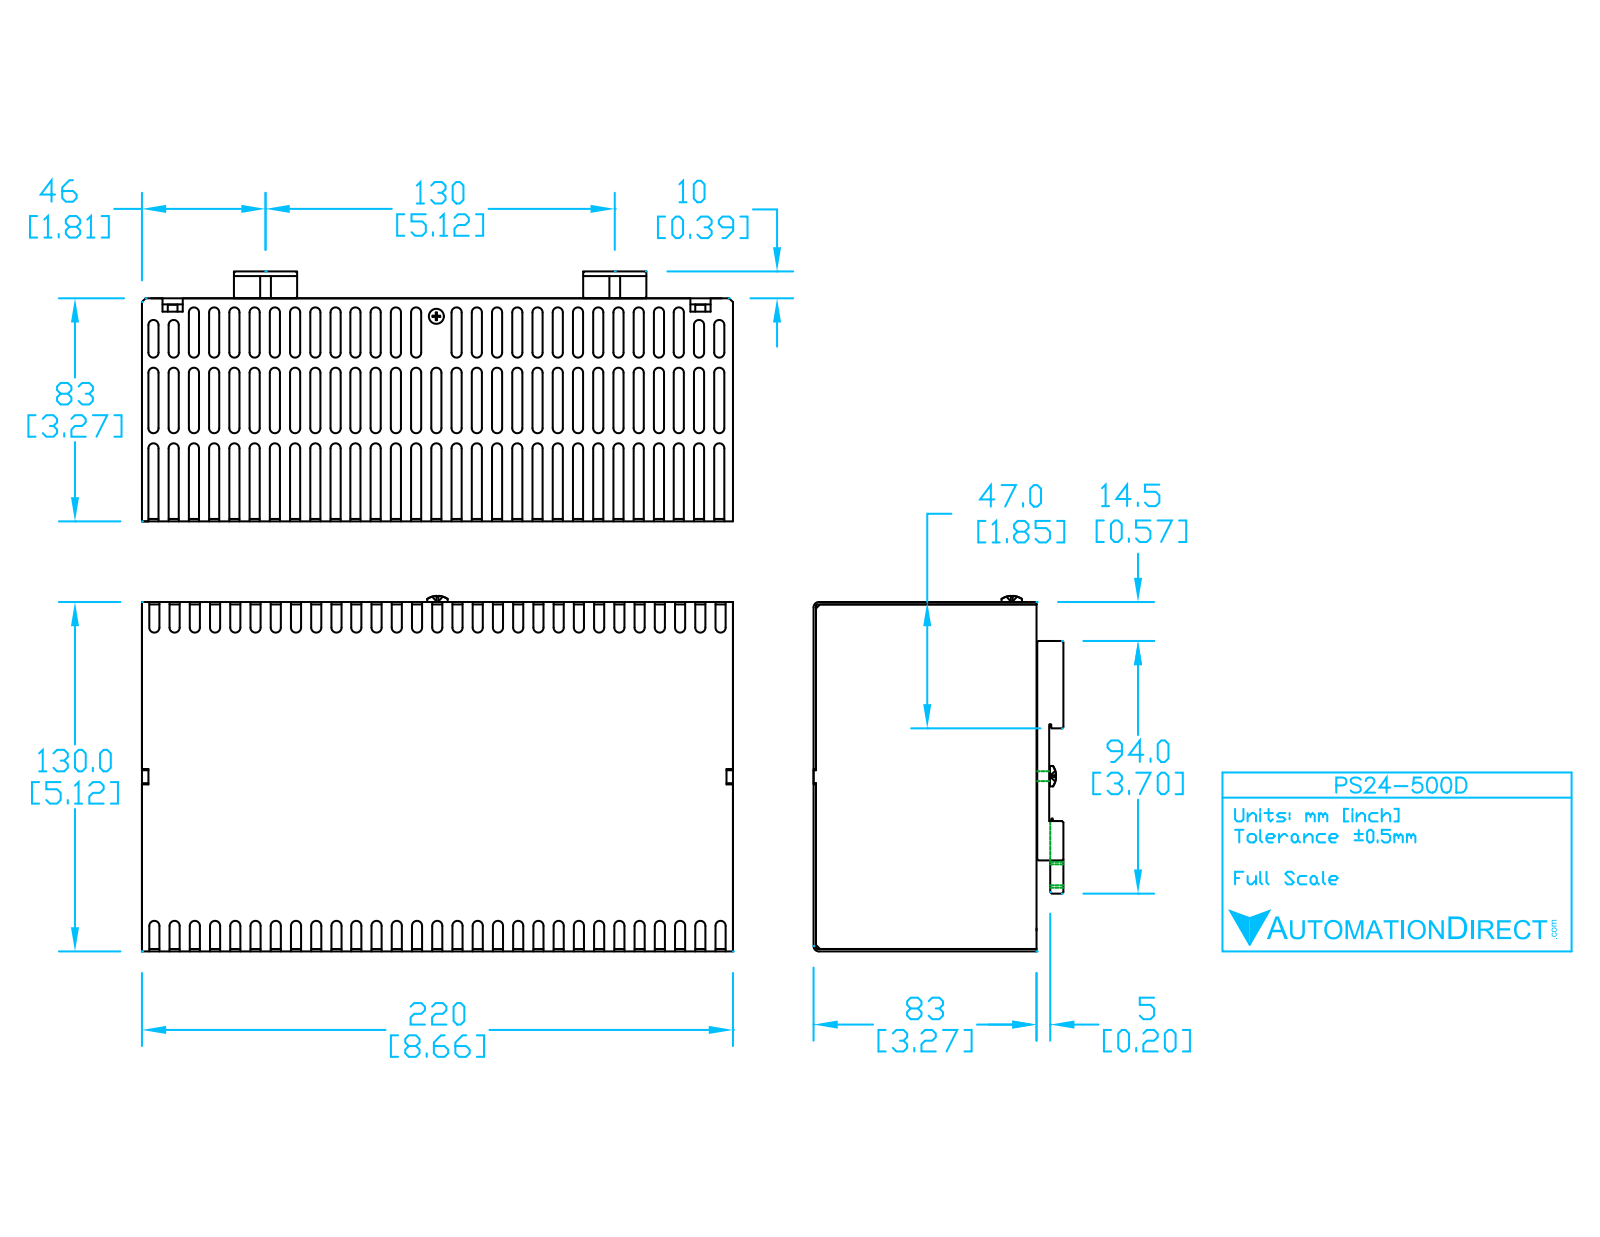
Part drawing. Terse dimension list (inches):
name: PS24-500D
written by: SolidWorks 2011 (CONFIG_CONTROL_DESIGN)
unit: in
bodies: 1 solid, 1523 faces (826 planar, 617 cylindrical, 80 other)
size: 8.66 × 5.627 × 3.734
volume: 77.82 in³; area: 327.5 in²
holes: 7× ⌀0.15
bosses: 2× ⌀0.265, 2× ⌀0.21, 1× ⌀0.3
rounds: 202× R0.074, 4× R0.06, 2× R0.015, 2× R0.02, 2× R0.05
face distances: 0.04, 5.08, 2.495, 3.269, 0.08, 3.189, 3.229, 3.149, 0.041, 3.805
hole spacings: 0.205, 0.3, 0.205, 0.41, 0.41, 0.6, 0.615, 5.754
